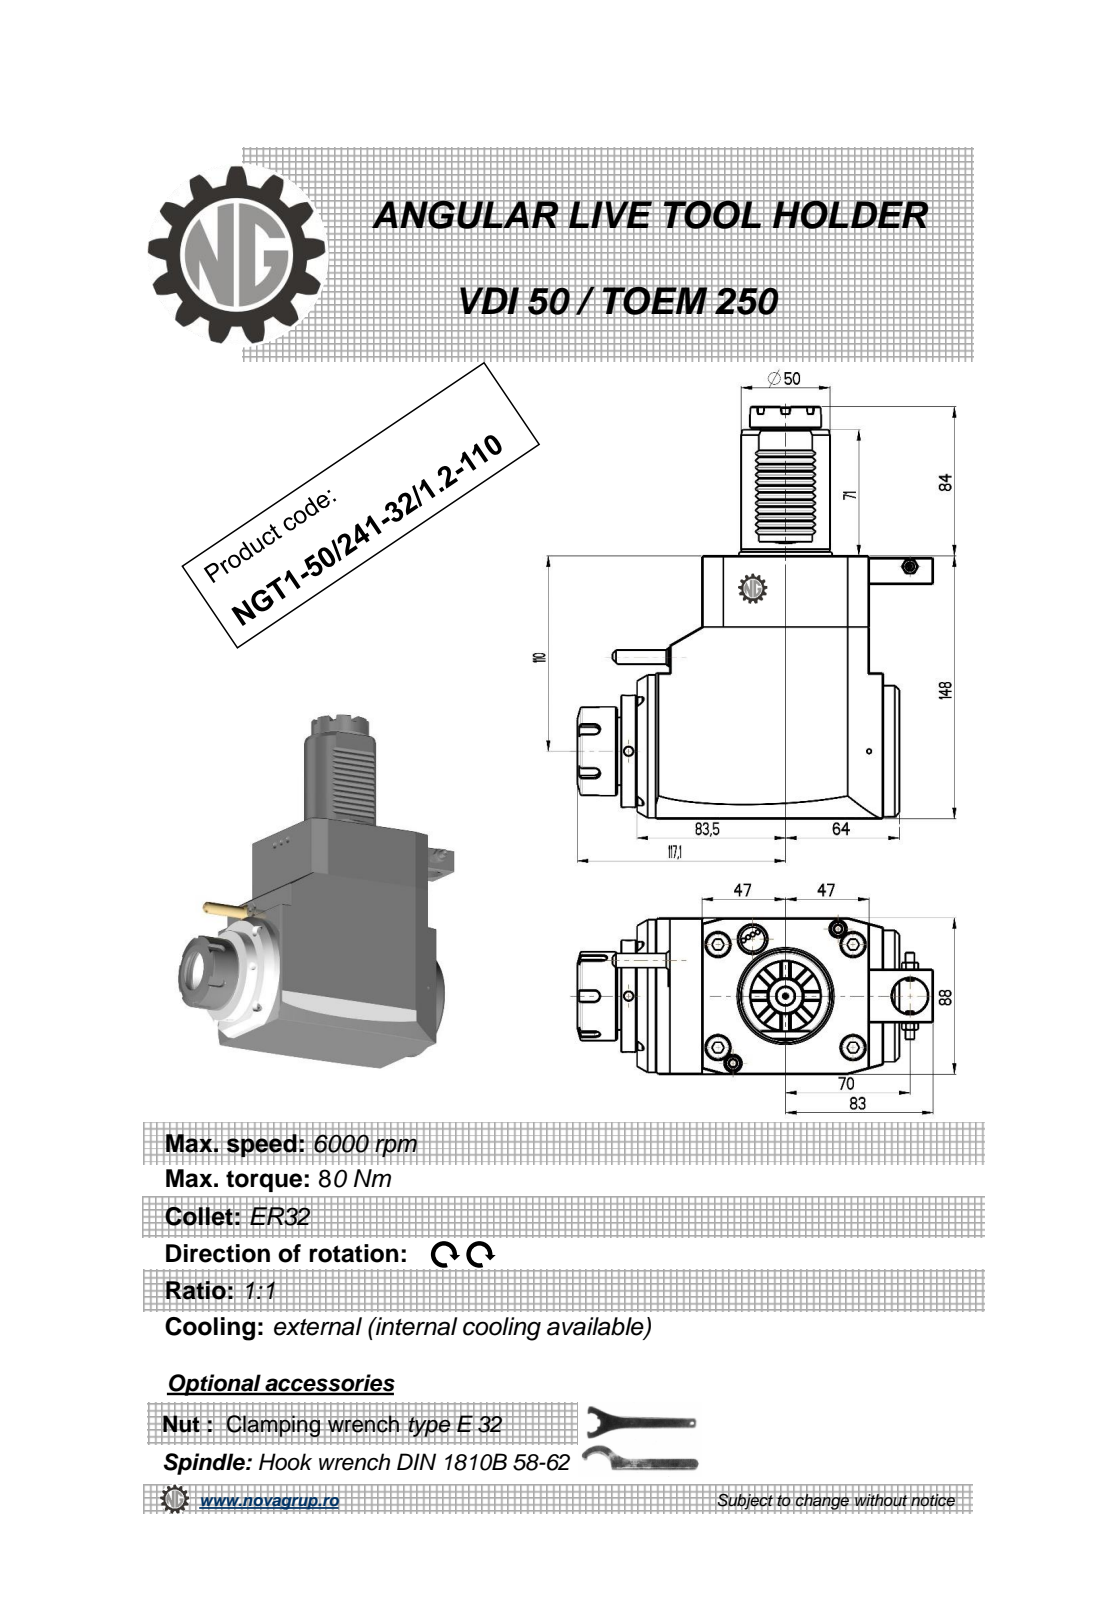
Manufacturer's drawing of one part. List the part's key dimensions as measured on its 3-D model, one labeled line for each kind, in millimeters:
Part name (STEP PRODUCT): NGT1_50_241_32_1_2_110
STEP written by: PRO/ENGINEER BY PARAMETRIC TECHNOLOGY CORPORATION, 2010280 (CONFIG_CONTROL_DESIGN)
Units: millimetres
Bodies: 1 solid, 480 faces (233 planar, 90 cylindrical, 157 other)
Overall size (bounding box): 232 × 200.1 × 88
Volume: 1 808 000 mm³ · Surface area: 113 909 mm²
Round holes (diameter × count): ⌀5 ×3, ⌀3 ×1, ⌀4.5 ×1, ⌀9.5 ×1, ⌀20 ×1, ⌀27 ×1
Round bosses / shafts (diameter × count): ⌀50 ×2, ⌀86 ×1, ⌀74 ×1, ⌀63 ×1, ⌀50.5 ×1, ⌀41 ×1, ⌀40 ×1, ⌀20.5 ×1
Partial cylindrical surfaces — rounded edges, fillets, slot ends (radius × count): R0.26 ×12, R0.3 ×12, R0.2 ×6, R3 ×5
Main face-to-face distances: 88, 148, 147.5, 9, 17, 8, 111, 94, 36.5, 130.5
Hole centre spacings: 52.46, 56.65, 101.5, 158.25
